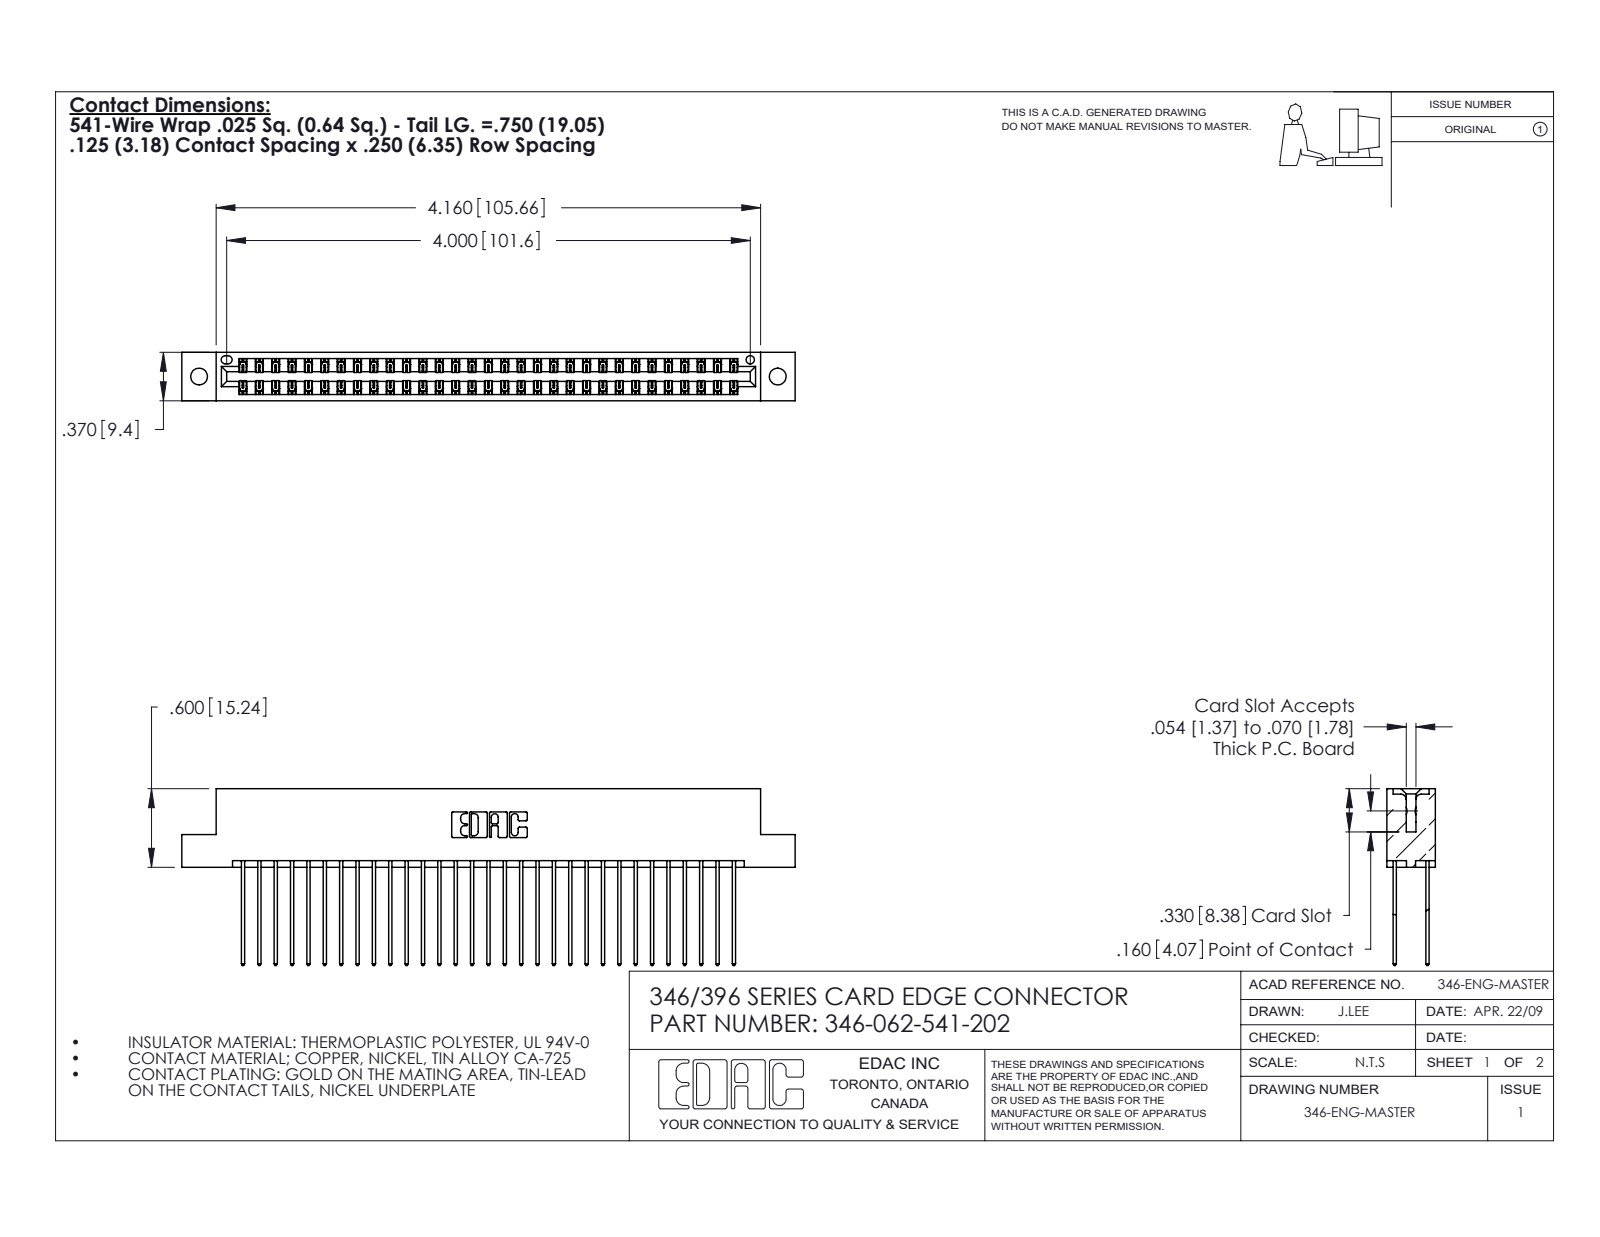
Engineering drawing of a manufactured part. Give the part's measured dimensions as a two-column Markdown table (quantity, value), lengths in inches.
| quantity | value |
| --- | --- |
| part name | 345-292-001_345-293-141; 346 Part_Flush Mounting Lugs - 0.128 Dia; 346-062-541-202 |
| STEP written by | SolidWorks 2020 (CONFIG_CONTROL_DESIGN) |
| units | inches |
| bodies | 63 solids, 3346 faces (2246 planar, 1100 cylindrical, 0 other) |
| overall size | 4.685 × 1.35 × 0.37 |
| volume | 0.722 in³ |
| surface area | 27.18 in² |
| round holes (diameter × count) | 0.128 × 2, 0.064 × 1 |
| partial cylindrical surfaces (radius × count) | 0.006 × 93, 0.01 × 62, 0.01 × 22, 0.007 × 6, 0.031 × 6, 0.026 × 3, 0.014 × 2, 0.022 × 2 |
| main face-to-face distances | 0.048, 0.322, 0.25, 0.072, 0.298, 0.025, 0.37, 0.275, 0.225, 0.148 |
| hole center spacings | 0.246, 4.212, 4.42 |
